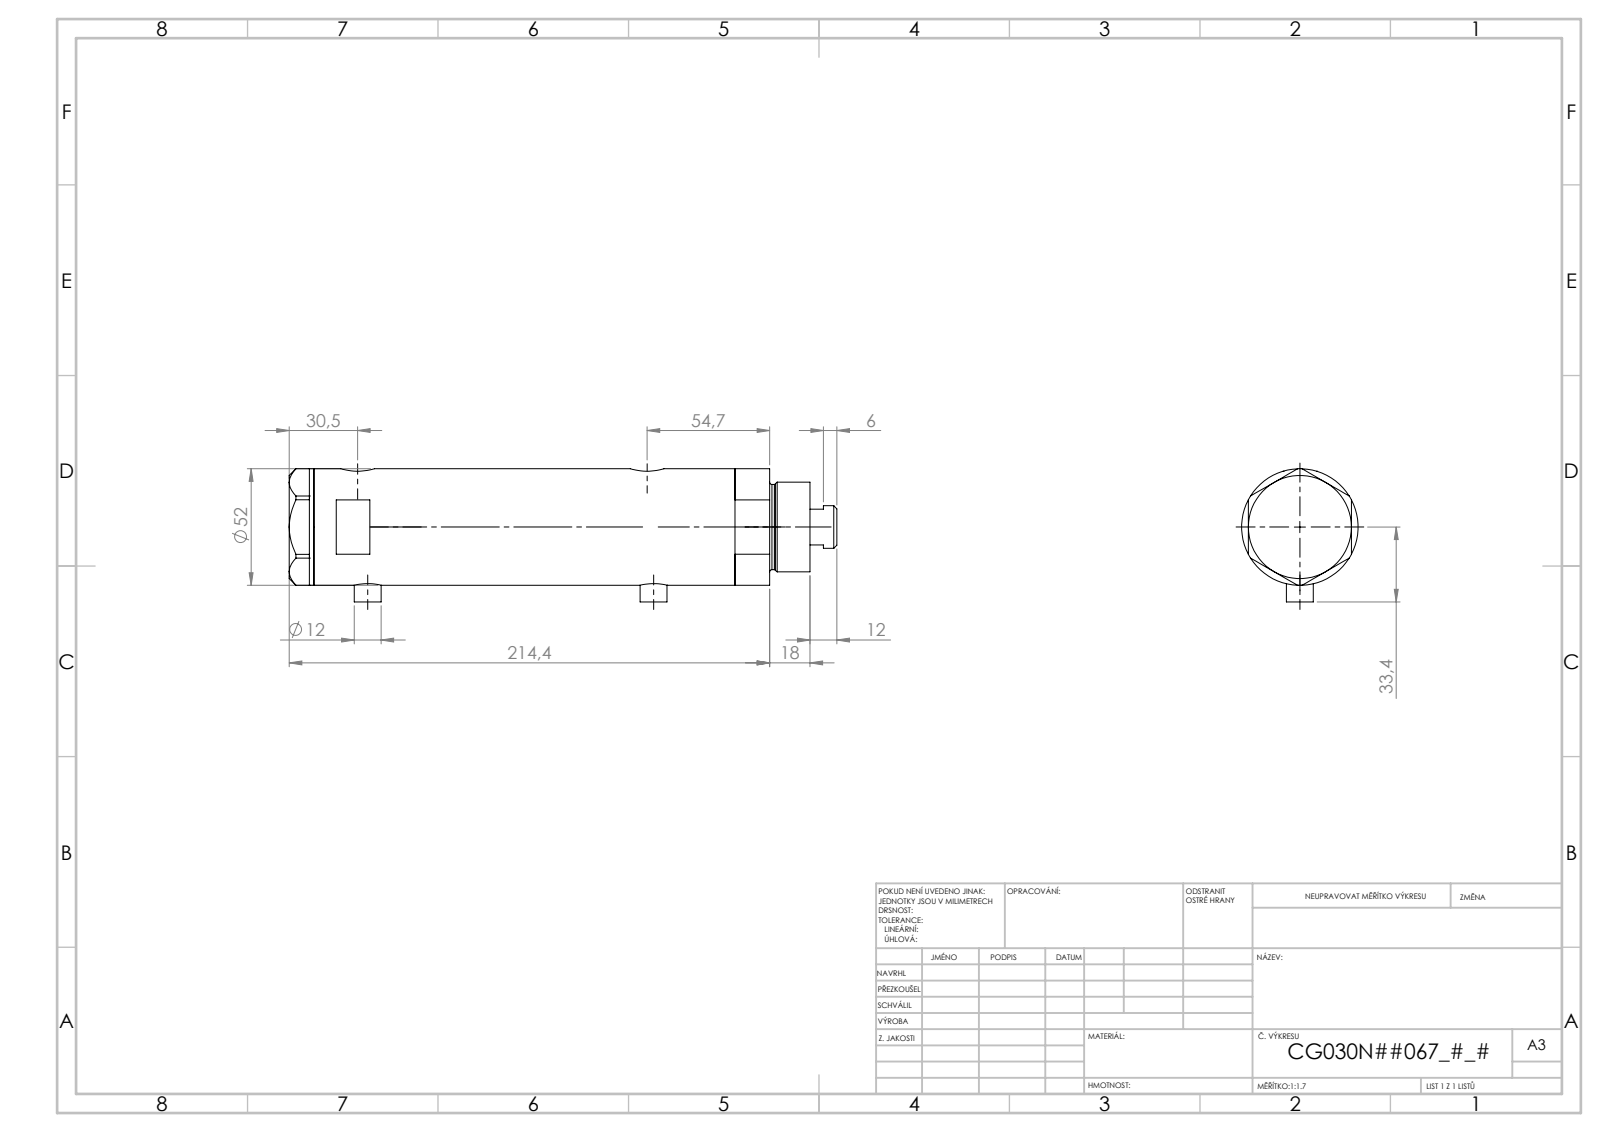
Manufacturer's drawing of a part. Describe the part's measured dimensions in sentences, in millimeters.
The part is named "V270CG_VC; V270CG_FRONT; V270CG_BACK; V270CG_MIDDLE". Its 3-D file was written by "SolidWorks 2019 (CONFIG_CONTROL_DESIGN)". It is 4 solids with 140 faces: 67 planar, 53 cylindrical and 20 other. Overall it measures 216.02 by 53.1 by 52 millimeters. Its volume is 383 497 cubic millimeters and its surface area 86 559 square millimeters. Round holes: 2 of diameter 5, 2 of diameter 9.73, 2 of diameter 12.5, 2 of diameter 15, 1 of diameter 6.5, 1 of diameter 20, 1 of diameter 21.5, 1 of diameter 30, 1 of diameter 33, 1 of diameter 44. Round bosses or shafts: 2 of diameter 12, 1 of diameter 52, 1 of diameter 40, 1 of diameter 38, 1 of diameter 19. The main face-to-face distances are 120.54, 23.8, 96.74, 11, 34.8, 131.54, 46, 167.94, 156.94, 133.14. The hole center spacings are 2.9, 4.5, 93.75, 96.65, 98.25, 101.15, 2.89, 2.91.
